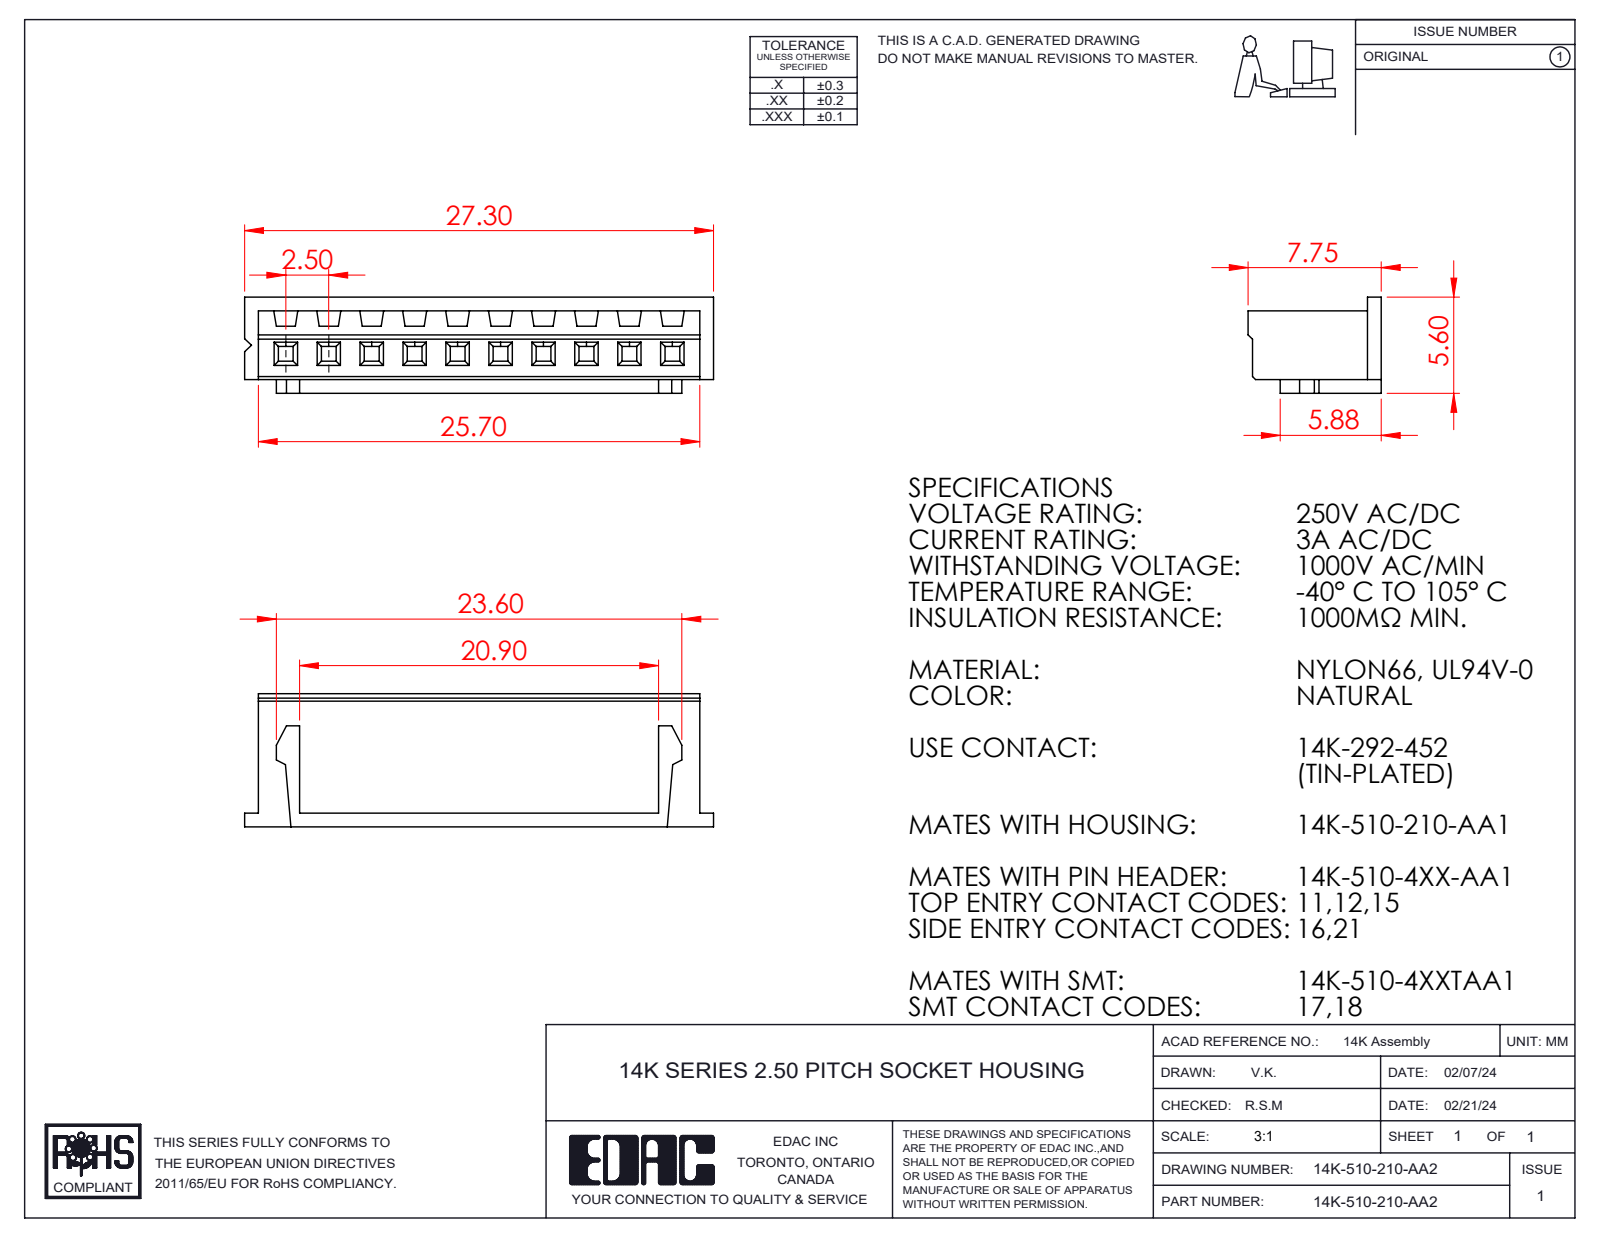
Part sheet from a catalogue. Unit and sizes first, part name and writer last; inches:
Units: inches
Overall size (bounding box): 1.075 × 0.305 × 0.22
Main face-to-face distances: 0.098, 0.295, 0.197, 0.394, 0.083, 0.024, 0.181, 0.492, 0.016, 0.133
Volume: 0.025 in³ · Surface area: 2.229 in²
Bodies: 1 solid, 250 faces (250 planar, 0 cylindrical, 0 other)
Part name (STEP PRODUCT): 14K-510-210-AA2
STEP written by: SolidWorks 2023 (CONFIG_CONTROL_DESIGN)
